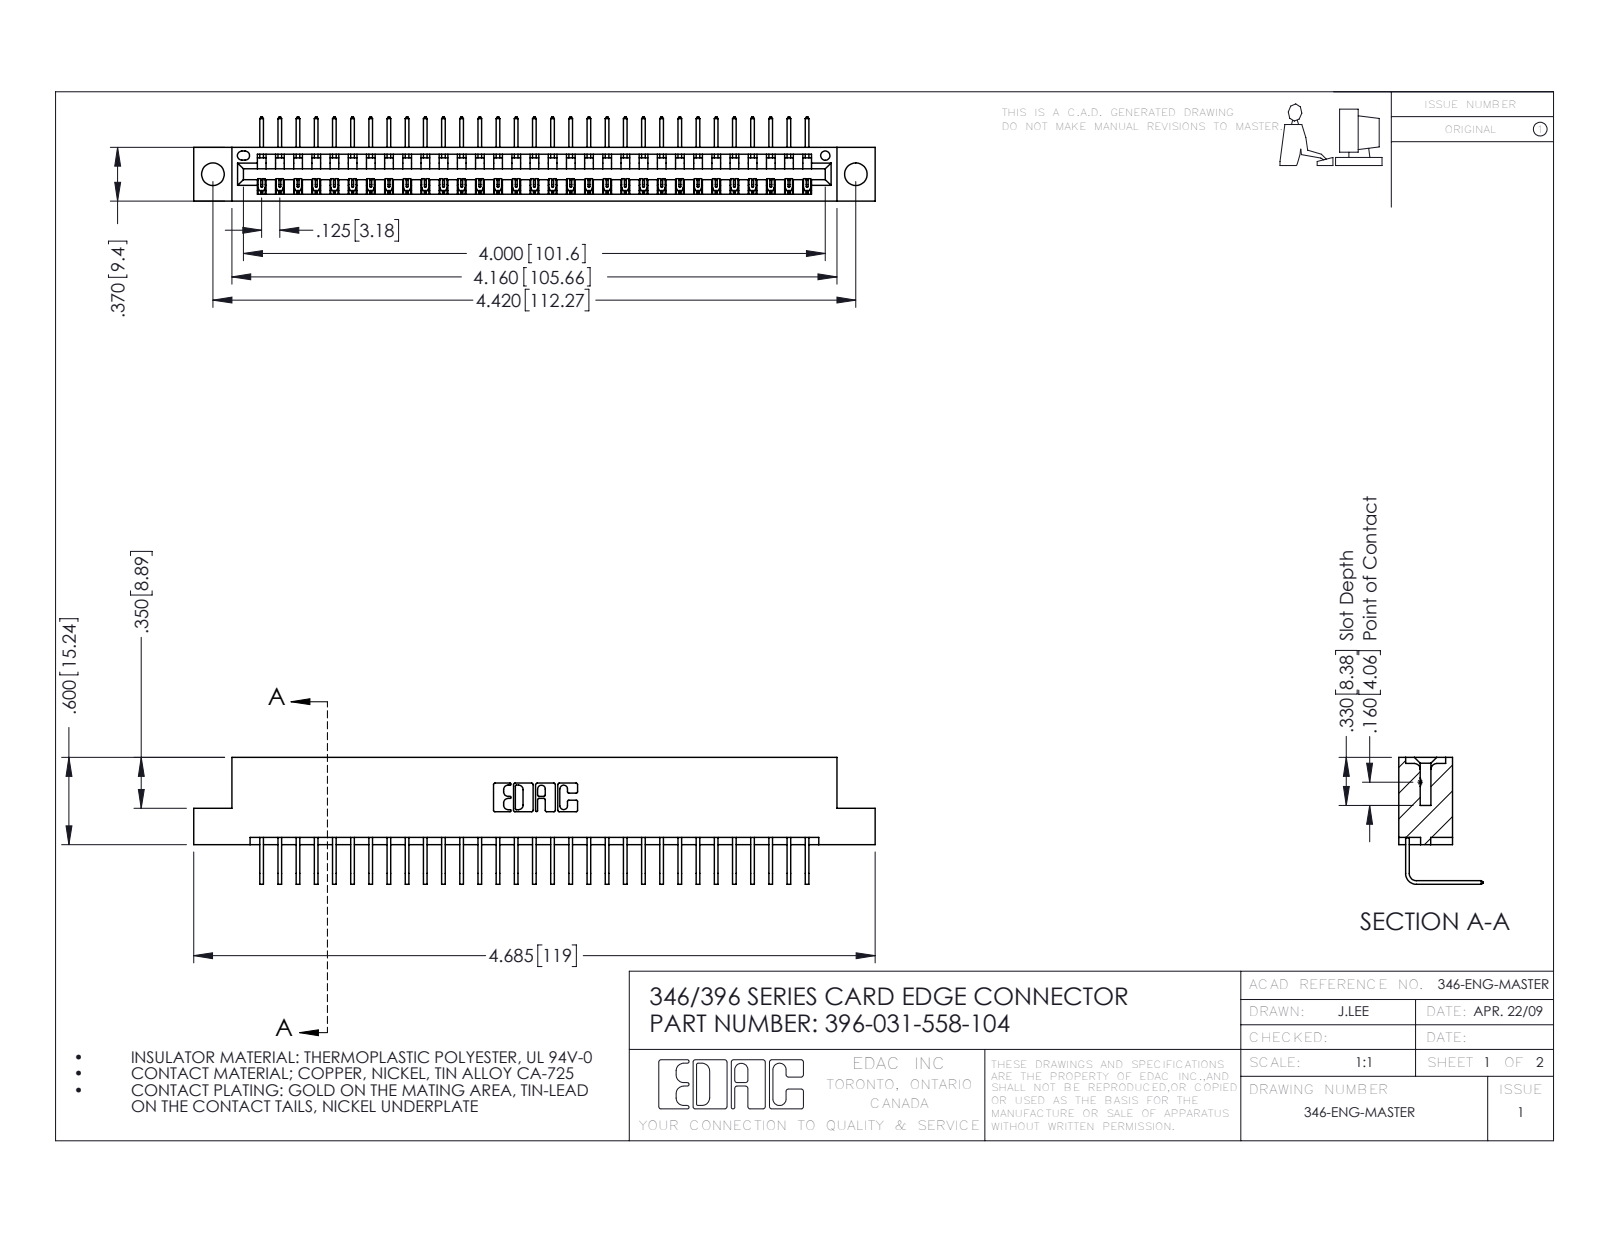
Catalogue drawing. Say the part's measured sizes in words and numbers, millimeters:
The part is named "396-031-558-104; 345-292-001_558 Tail - 2; 346 Part_Flush Mounting Lugs - 0.156 Dia-TH". Its 3-D file was written by "SolidWorks 2016 (CONFIG_CONTROL_DESIGN)". It is 32 solids with 1982 faces: 1378 planar, 604 cylindrical and 0 other. Overall it measures 119 by 22.2 by 14.7 millimeters. Its volume is 11 300 cubic millimeters and its surface area 14 460 square millimeters. Round holes: 2 of diameter 4, 1 of diameter 1.6. Partial cylindrical surfaces (rounded edges, fillets, slot ends): 62 of radius 0.2, 22 of radius 0.3, 6 of radius 0.2, 6 of radius 0.8, 3 of radius 0.7, 2 of radius 0.8, 2 of radius 1, 1 of radius 0.4. The main face-to-face distances are 8.2, 1.2, 9.4, 6.4, 7.6, 0.6, 1.8, 3.8, 5.6, 2.5. The hole center spacings are 6.2, 107, 112.3.
